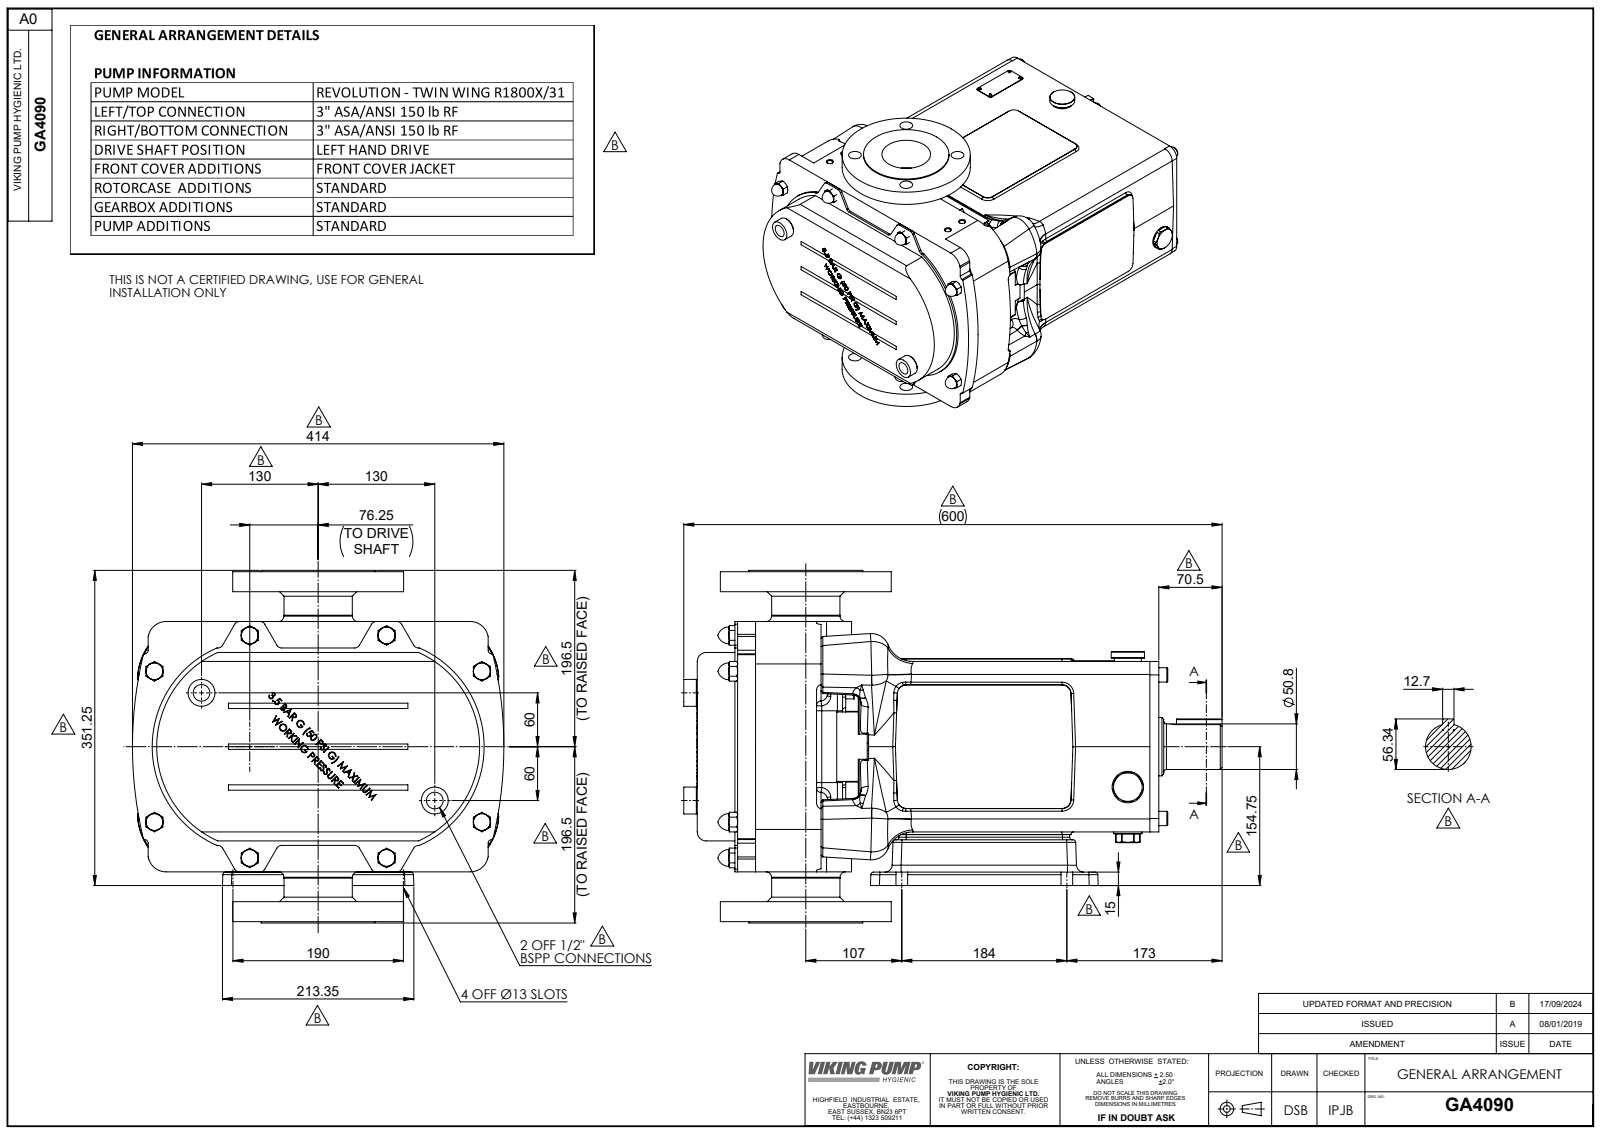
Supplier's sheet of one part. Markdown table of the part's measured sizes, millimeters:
| quantity | value |
| --- | --- |
| part name | Copy of R1800 CPP V LHD^GA4090; Copy of Frame 5 Bolt on Jacket^GA4090; GA4090; Copy of Z94-5301-55 - 3 INCH ASA 150^GA4090 |
| STEP written by | SolidWorks 2023 (AUTOMOTIVE_DESIGN) |
| units | millimeters |
| bodies | 5 solids, 2417 faces (979 planar, 472 cylindrical, 966 other) |
| overall size | 600 × 414 × 393 |
| volume | 41 400 000 mm³ |
| surface area | 1 558 000 mm² |
| round holes (diameter × count) | 19 × 6, 8.5 × 4, 13.5 × 4, 18.6 × 2, 26.2 × 2, 149 × 2, 35 × 1, 72.3 × 1 |
| round bosses / shafts (diameter × count) | 14 × 10, 8 × 10, 16 × 6, 18 × 4, 30 × 3, 187 × 2, 140 × 2, 106 × 2 |
| partial cylindrical surfaces (radius × count) | 6 × 52, 3 × 44, 10 × 32, 0.2 × 24, 1 × 16, 5 × 16, 4 × 14, 8 × 10 |
| main face-to-face distances | 45, 190, 469.5, 514.5, 349, 120.5, 165.5, 44.5, 234.5, 33.2 |
| hole center spacings | 76.2, 107.76, 124, 152.4, 196.55, 248, 152.5, 30 |
